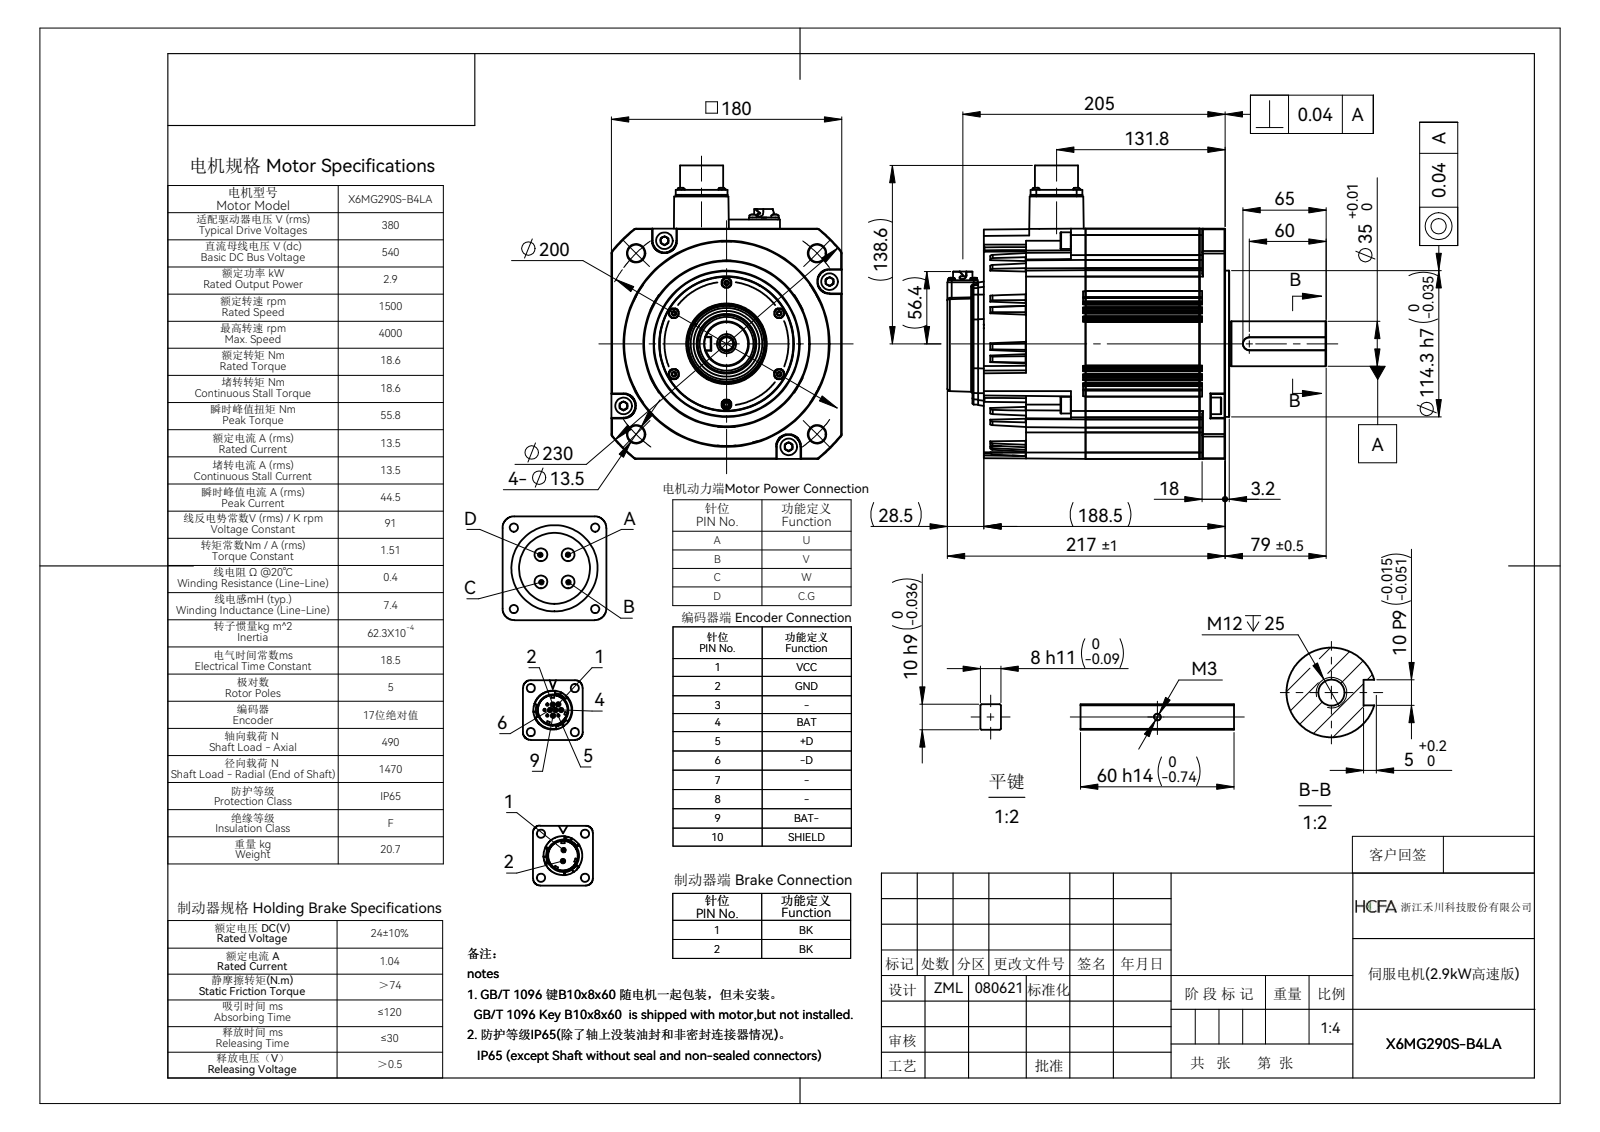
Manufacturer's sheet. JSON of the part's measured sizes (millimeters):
{"part_name": "SV-X2MG290S-B4LA", "step_written_by": "SolidWorks 2016 (CONFIG_CONTROL_DESIGN)", "units": "millimeters", "bodies": {"solids": 1, "faces": 3045, "planar": 1055, "cylindrical": 982, "other": 1008}, "overall_size": [296, 229.25, 180], "volume_mm3": 5433000, "surface_area_mm2": 273467, "round_holes": [[2.5, 20], [3.2, 12], [4.5, 6], [8, 6], [3.5, 4], [6.8, 4], [9, 4], [13.5, 4], [16, 3], [11.6, 2], [3.3, 1], [5, 1]], "round_bosses_or_shafts": [[1, 10], [3, 8], [13, 6], [8, 6], [7, 5], [4, 5], [5.7, 4], [5.6, 4]], "partial_cylinders_radius": [[0.5, 111], [1, 58], [5, 29], [2, 17], [0.55, 16], [0.2, 8], [3, 8], [2.8, 4]], "face_to_face_distances": [180, 32.5, 188.5, 147.5, 4, 115, 184.5, 3, 7, 28.5], "hole_center_spacings": [47.5, 12.16, 17.2, 114.13, 63.79, 78.87, 5.96, 15.31]}
